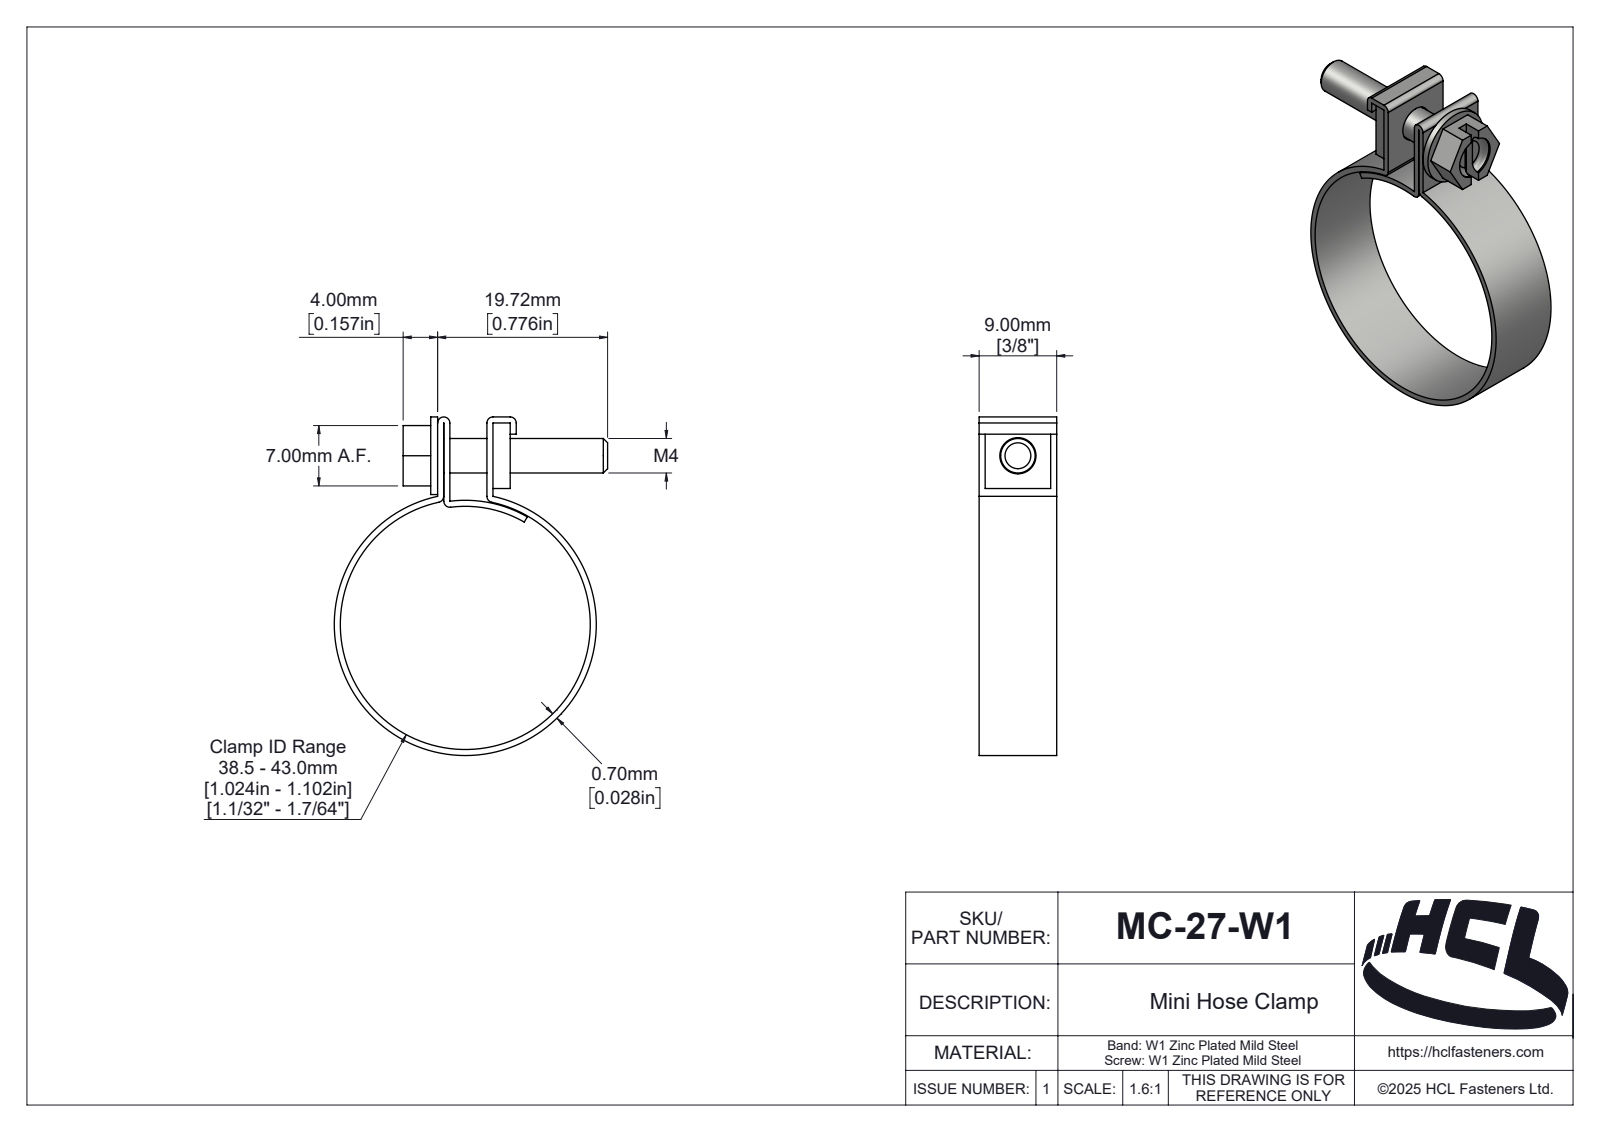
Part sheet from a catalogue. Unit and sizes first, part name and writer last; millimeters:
Units: millimetres
Overall size (bounding box): 39.26 × 31.71 × 9
Round holes (diameter × count): ⌀4.2 ×1, ⌀5 ×1, ⌀29 ×1
Round bosses / shafts (diameter × count): ⌀30.4 ×1, ⌀9 ×1, ⌀4 ×1
Partial cylindrical surfaces — rounded edges, fillets, slot ends (radius × count): R0.7 ×5, R0.2 ×1, R0.71 ×1, R0.81 ×1, R1.01 ×1, R1.06 ×1, R1.28 ×1, R1.81 ×1
Main face-to-face distances: 0.7, 5, 0.72, 5.72, 6.42, 7, 9, 2, 2.7, 8.42
Volume: 1 277 mm³ · Surface area: 3 137 mm²
Bodies: 3 solids, 170 faces (38 planar, 79 cylindrical, 53 other)
Part name (STEP PRODUCT): MC-27-W1
STEP written by: SolidWorks 2025 (AUTOMOTIVE_DESIGN)
